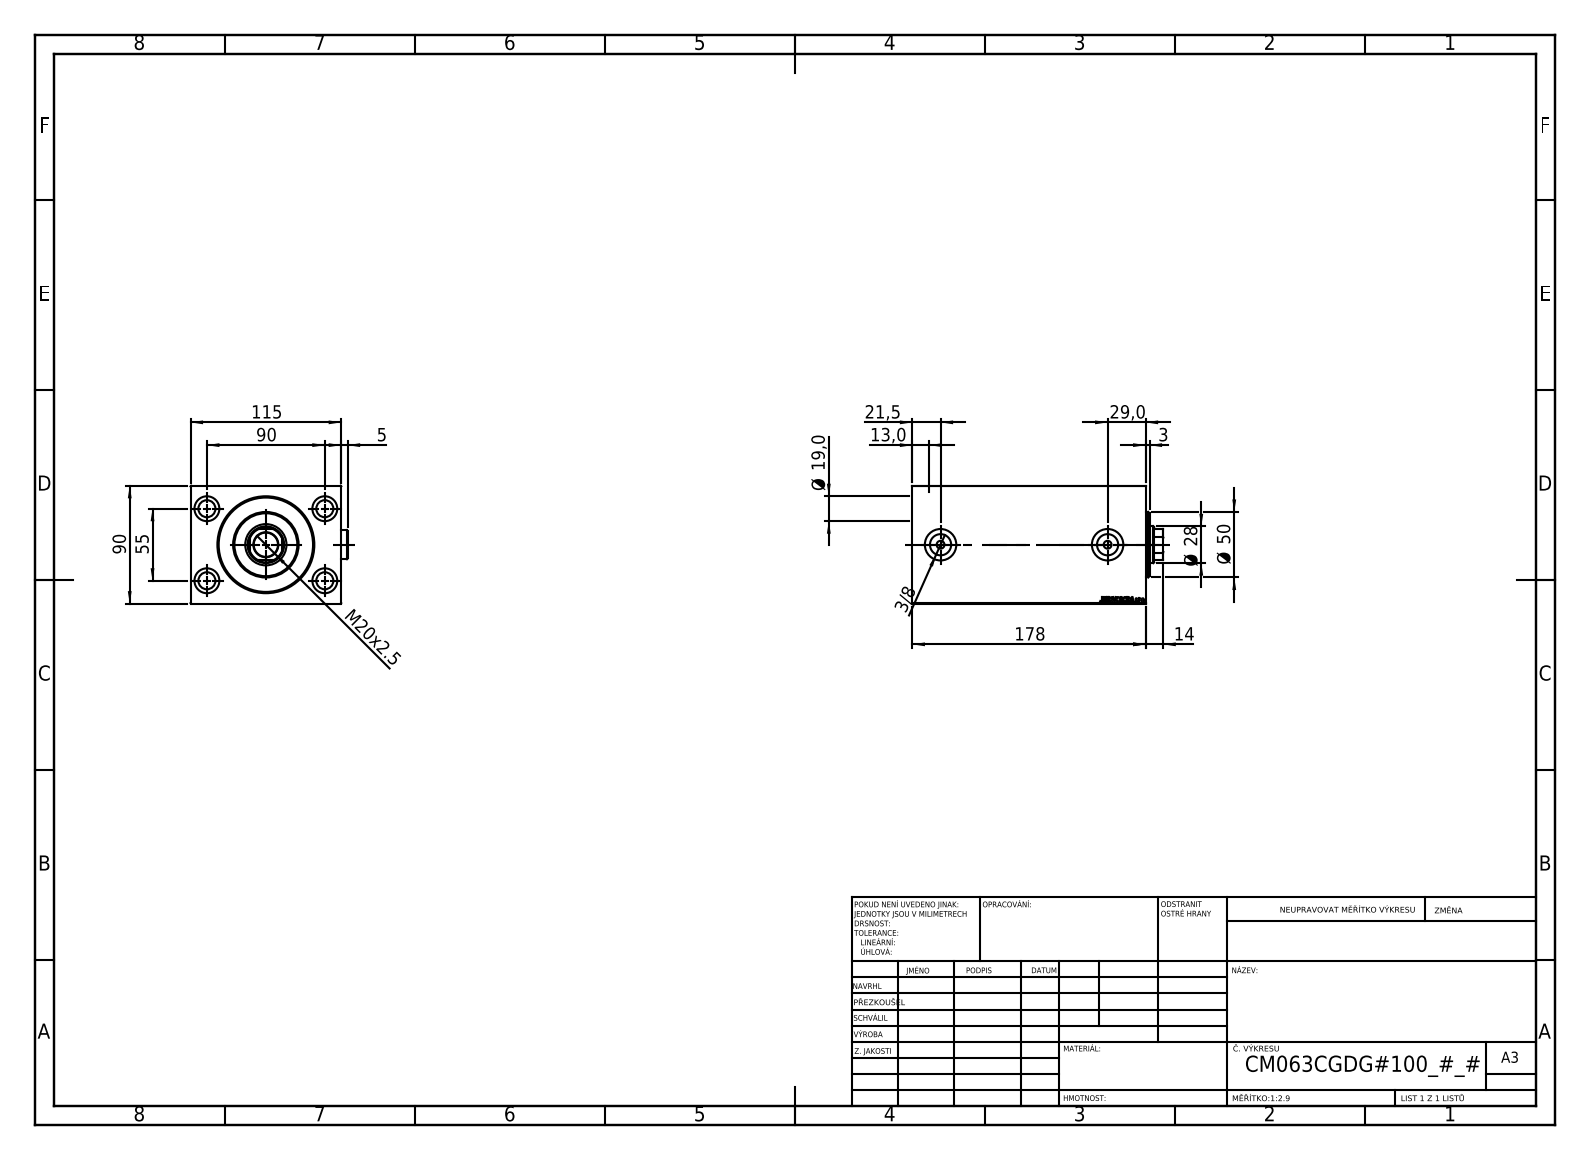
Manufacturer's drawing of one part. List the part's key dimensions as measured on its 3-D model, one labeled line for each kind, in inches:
Part name (STEP PRODUCT): V450CM_C_Body; V450CM_VC_B; V450CM_C_VCP; Zatka_OIL_PORT
STEP written by: SolidWorks 2019 (CONFIG_CONTROL_DESIGN)
Units: inches
Bodies: 5 solids, 919 faces (443 planar, 78 cylindrical, 398 other)
Overall size (bounding box): 7.539 × 4.72 × 3.543
Volume: 90.13 in³ · Surface area: 311.4 in²
Round holes (diameter × count): ⌀0.512 ×4, ⌀0.748 ×4, ⌀0.236 ×2, ⌀0.637 ×2, ⌀0.945 ×2, ⌀0.728 ×1, ⌀1.102 ×1, ⌀1.24 ×1, ⌀2.48 ×1, ⌀2.559 ×1, ⌀2.835 ×1
Round bosses / shafts (diameter × count): ⌀0.866 ×2, ⌀1.969 ×1
Partial cylindrical surfaces — rounded edges, fillets, slot ends (radius × count): R0.531 ×1
Main face-to-face distances: 3.543, 4.528, 7.008, 0.689, 6.319, 0.531, 5.787, 6.476, 4.469, 2.539
Hole centre spacings: 2.076, 2.165, 3.543, 4.153, 5.02
